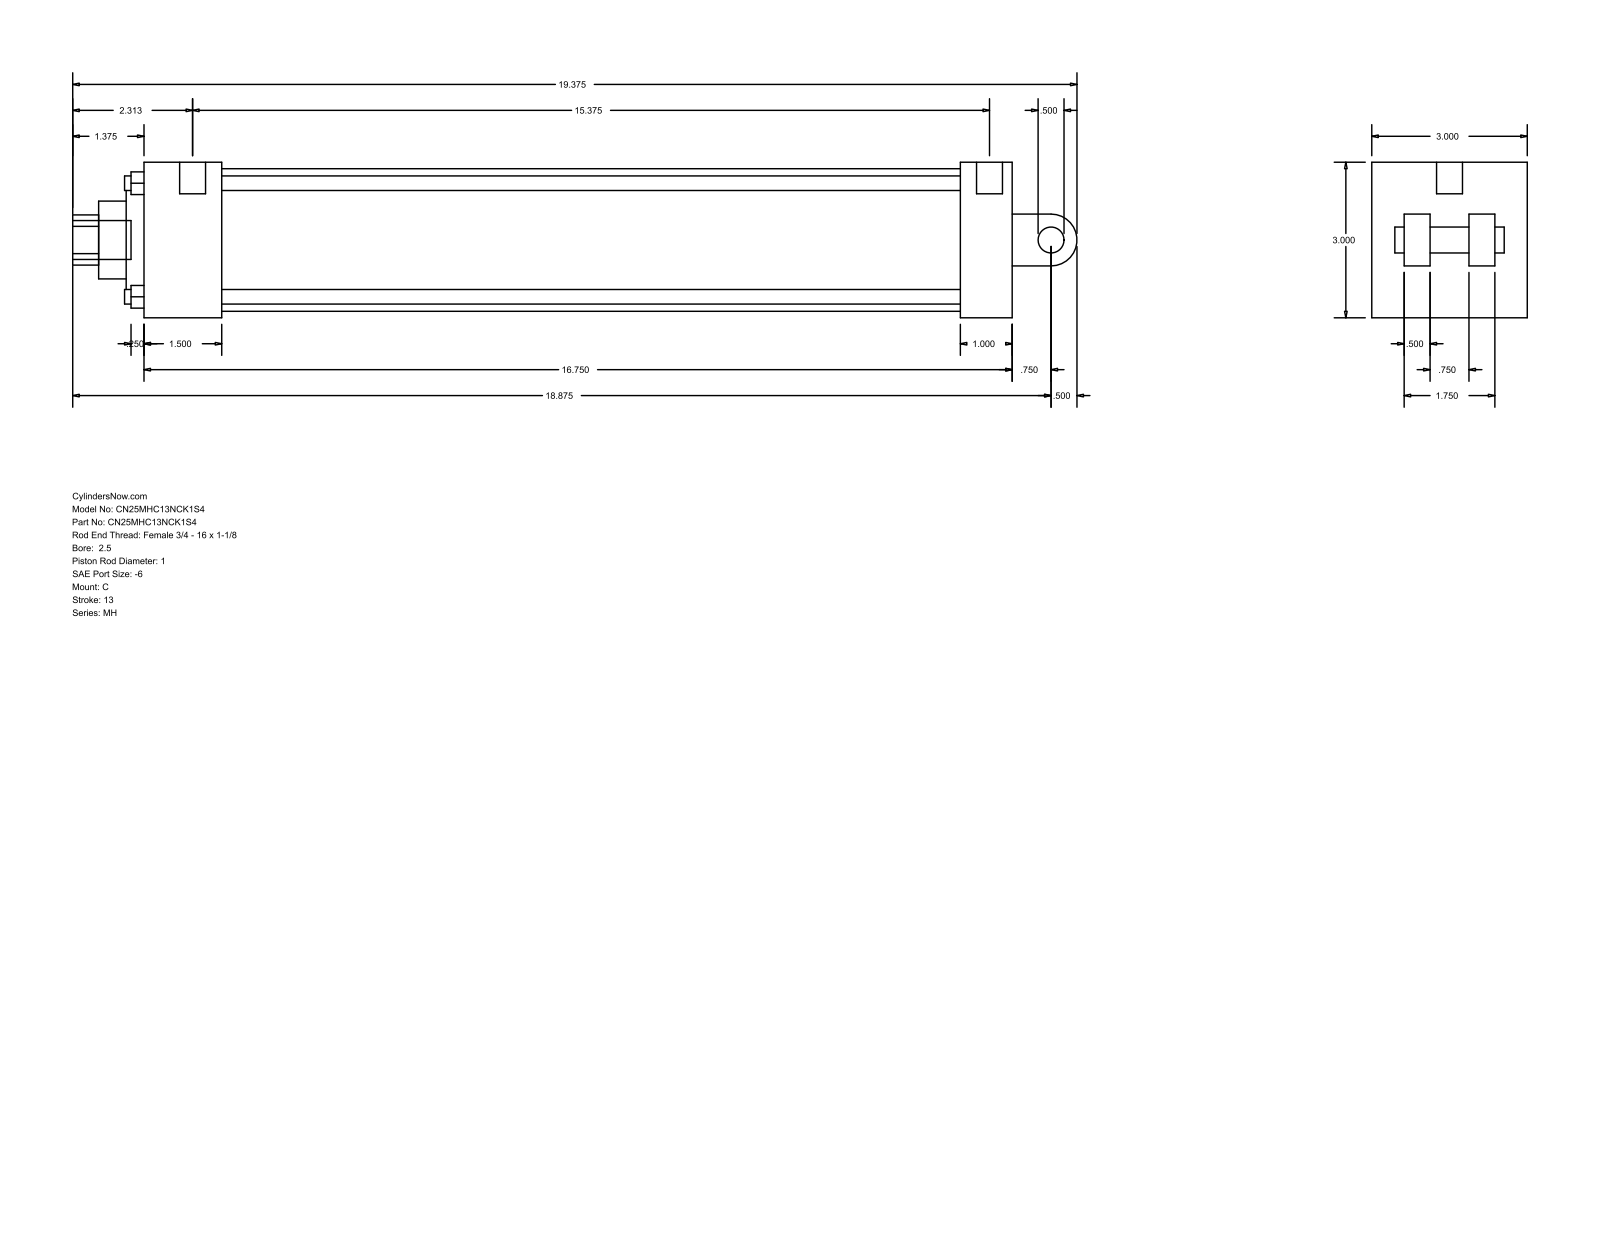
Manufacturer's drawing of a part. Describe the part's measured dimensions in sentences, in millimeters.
The part is named "MH_C__0250_1". Its 3-D file was written by "GSSL Pune (CONFIG_CONTROL_DESIGN)". It is 0 solids with 101 faces: 71 planar, 30 cylindrical and 0 other. Overall it measures 492.12 by 76.2 by 76.2 millimeters. Round holes: 4 of diameter 7.14, 2 of diameter 5.56, 1 of diameter 12.7, 1 of diameter 25.4, 1 of diameter 38.1, 1 of diameter 60.33, 1 of diameter 69.85. Round bosses or shafts: 2 of diameter 12.7, 2 of diameter 5.56, 1 of diameter 19.05. Partial cylindrical surfaces (rounded edges, fillets, slot ends): 1 of radius 12.29, 1 of radius 12.7. The main face-to-face distances are 76.2, 25.4, 425.46, 15.87, 60.33, 400.06, 38.11, 361.95, 387.35, 12.7. The hole center spacings are 39.33, 55.62, 78.66, 3.18.
